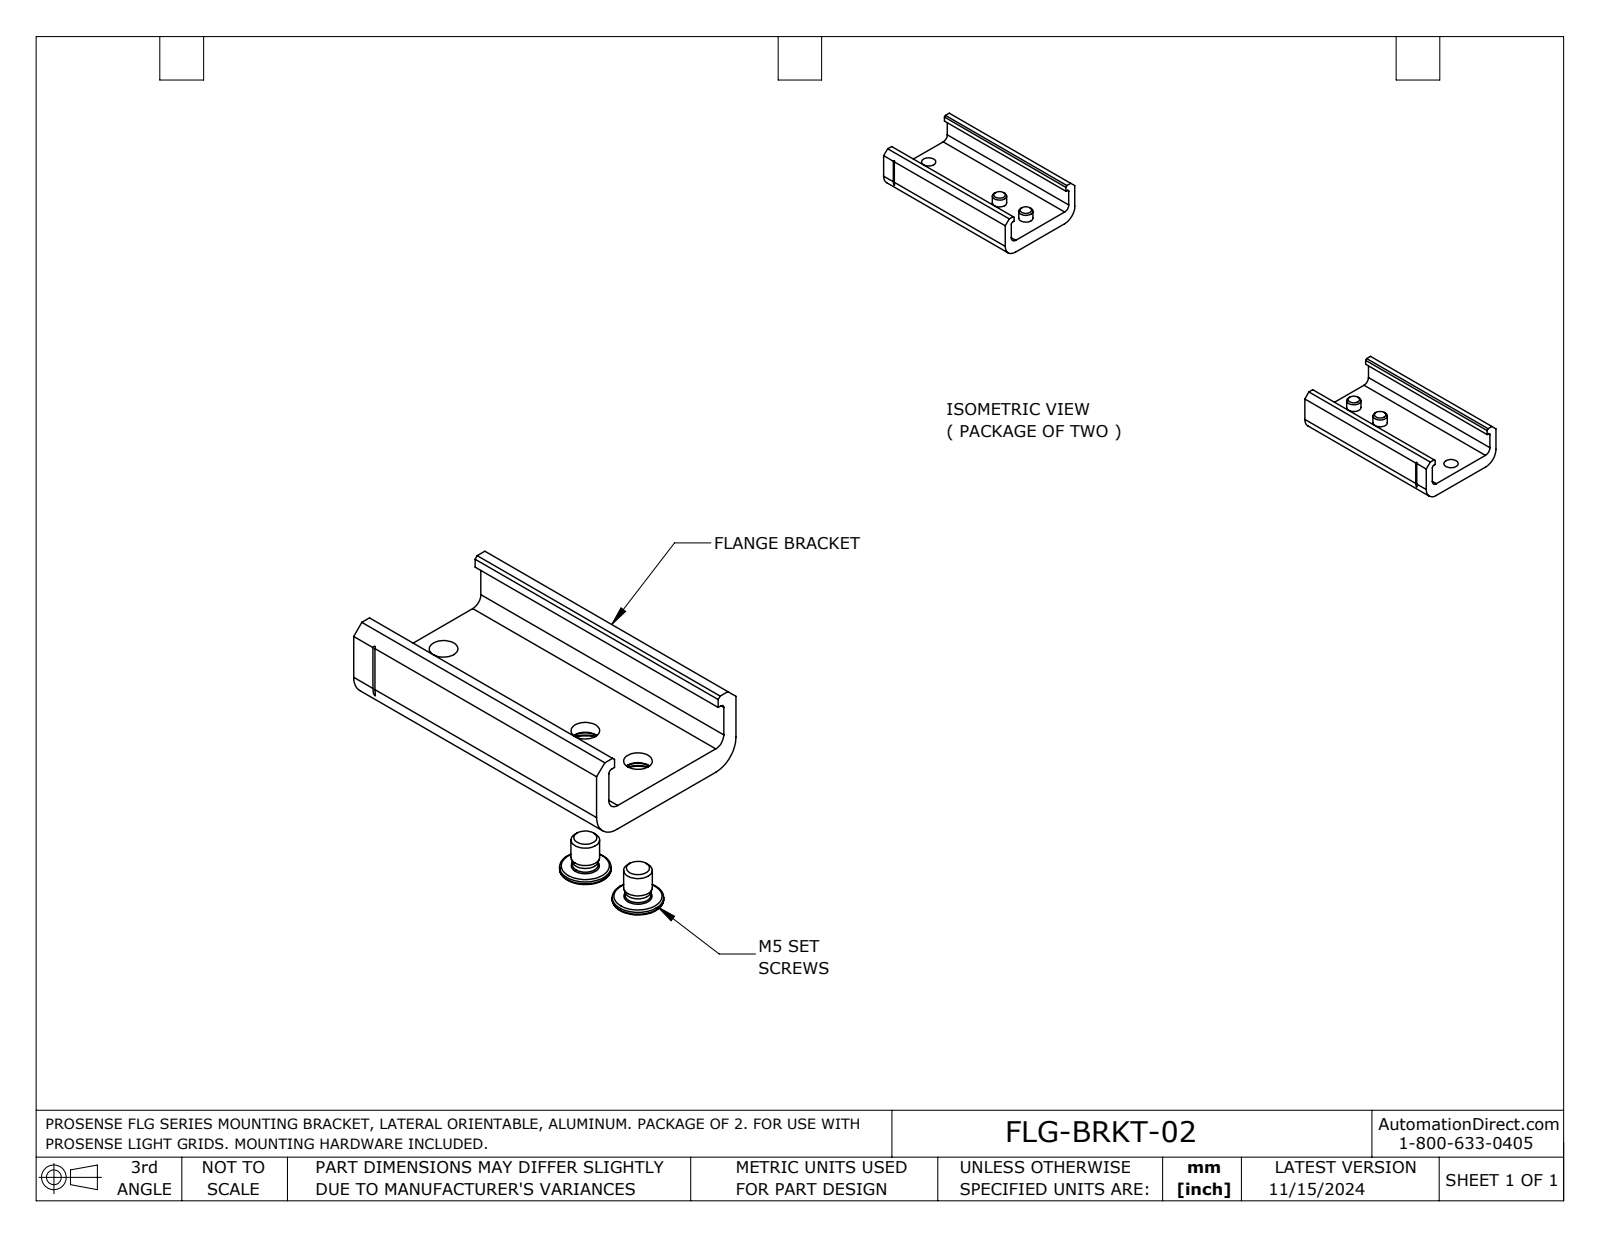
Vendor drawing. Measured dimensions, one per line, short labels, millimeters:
name: FLG-BRKT-02
written by: SolidWorks 2023 (AUTOMOTIVE_DESIGN)
unit: mm
bodies: 6 solids, 176 faces (104 planar, 38 cylindrical, 34 other)
size: 268 × 34.4 × 15.7
volume: 27 010 mm³; area: 16 460 mm²
holes: 6× ⌀5, 4× ⌀10
bosses: 4× ⌀9, 4× ⌀4.5
rounds: 4× R0.3, 2× R0.7, 2× R2, 2× R2.2, 2× R5
face distances: 5, 3, 31.4, 34.4, 28.4, 1.4, 60, 208, 15.7, 10.7
hole spacings: 13, 35, 48, 175, 210, 223, 162, 188
